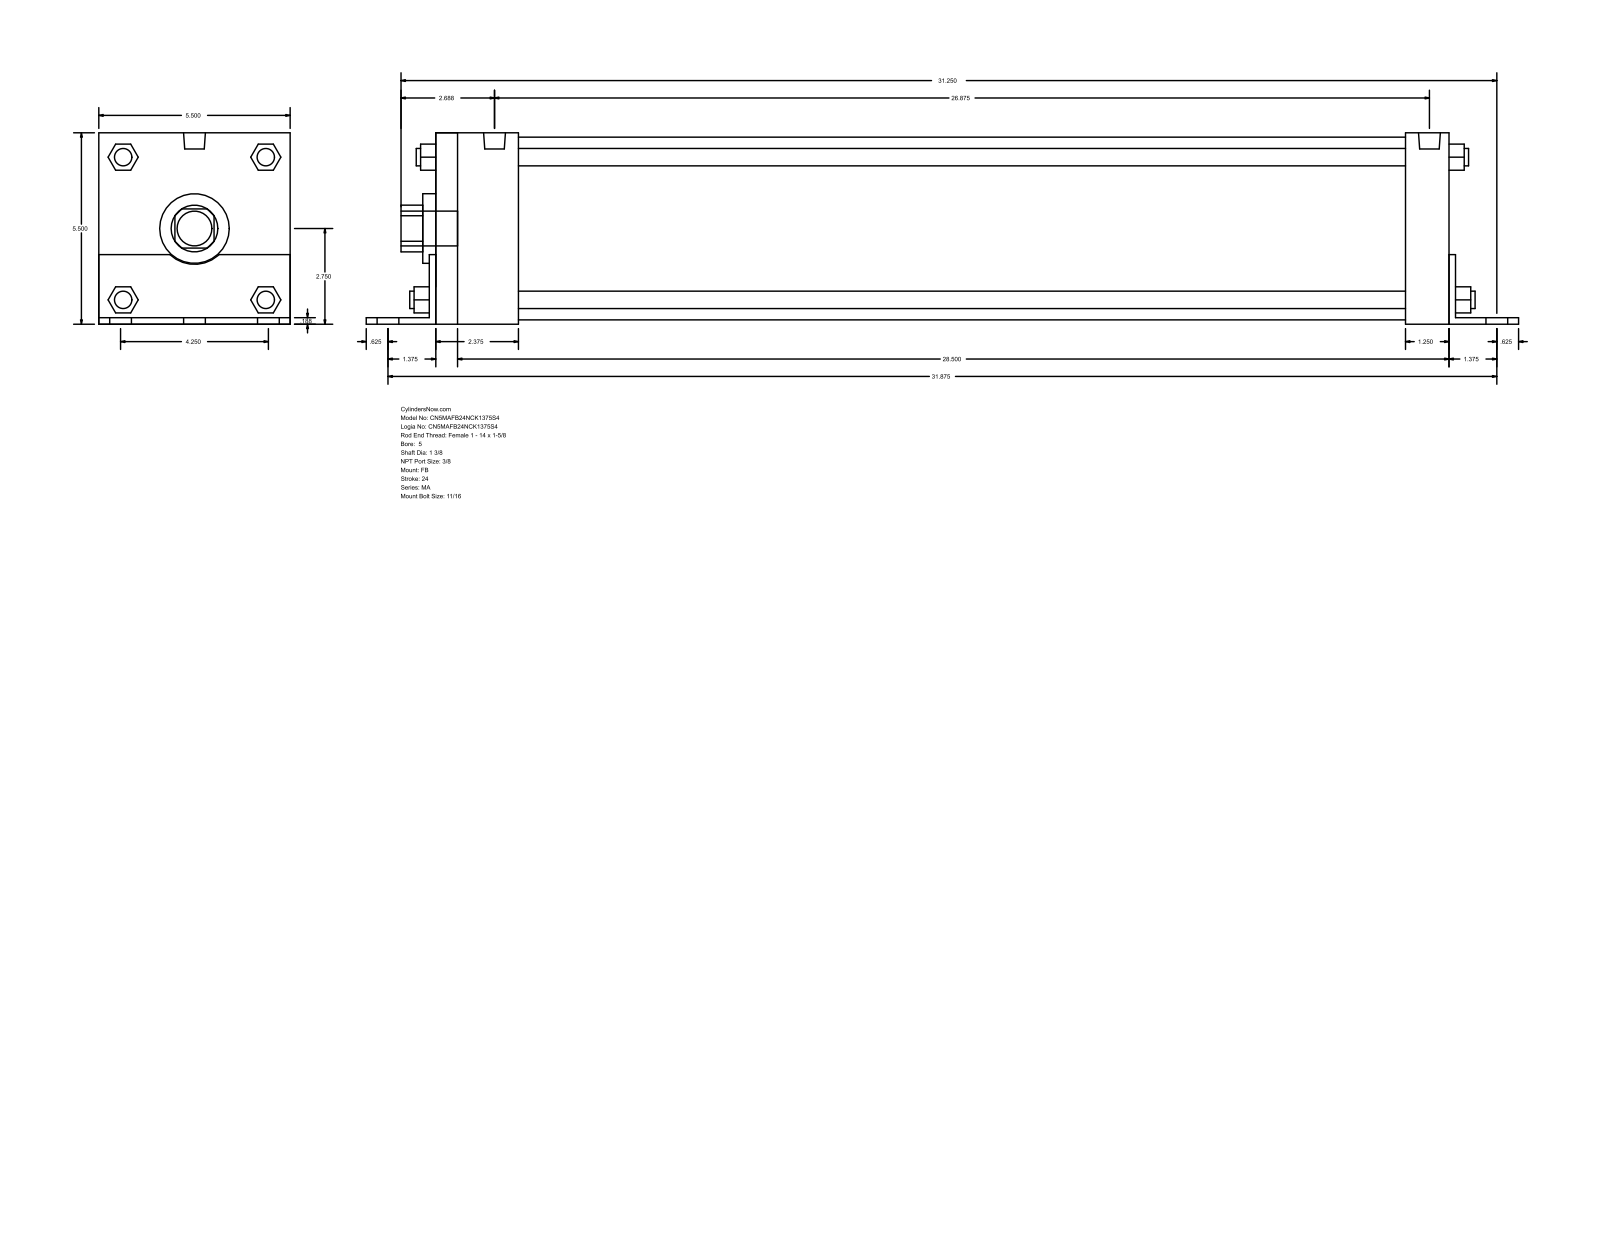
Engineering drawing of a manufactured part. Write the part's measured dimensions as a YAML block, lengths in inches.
part_name: "MA_FB__0500_1.375"
step_written_by: "GSSL Pune (CONFIG_CONTROL_DESIGN)"
units: inches
bodies: {solids: 0, faces: 140, planar: 105, cylindrical: 35, other: 0}
overall_size: [33.125, 5.502, 5.5]
round_holes:
  - {diameter: 1.375, count: 1}
  - {diameter: 2, count: 1}
  - {diameter: 5.25, count: 1}
round_bosses_or_shafts:
  - {diameter: 0.687, count: 6}
  - {diameter: 0.5, count: 4}
  - {diameter: 0.437, count: 4}
  - {diameter: 0.627, count: 2}
  - {diameter: 1, count: 1}
partial_cylinders:
  - {radius: 0.672, count: 1}
  - {radius: 1.03, count: 1}
face_to_face_distances: [5.5, 0.187, 5.502, 0.185, 5.315, 29.125, 0.188, 29.313, 29.312, 29.5]
